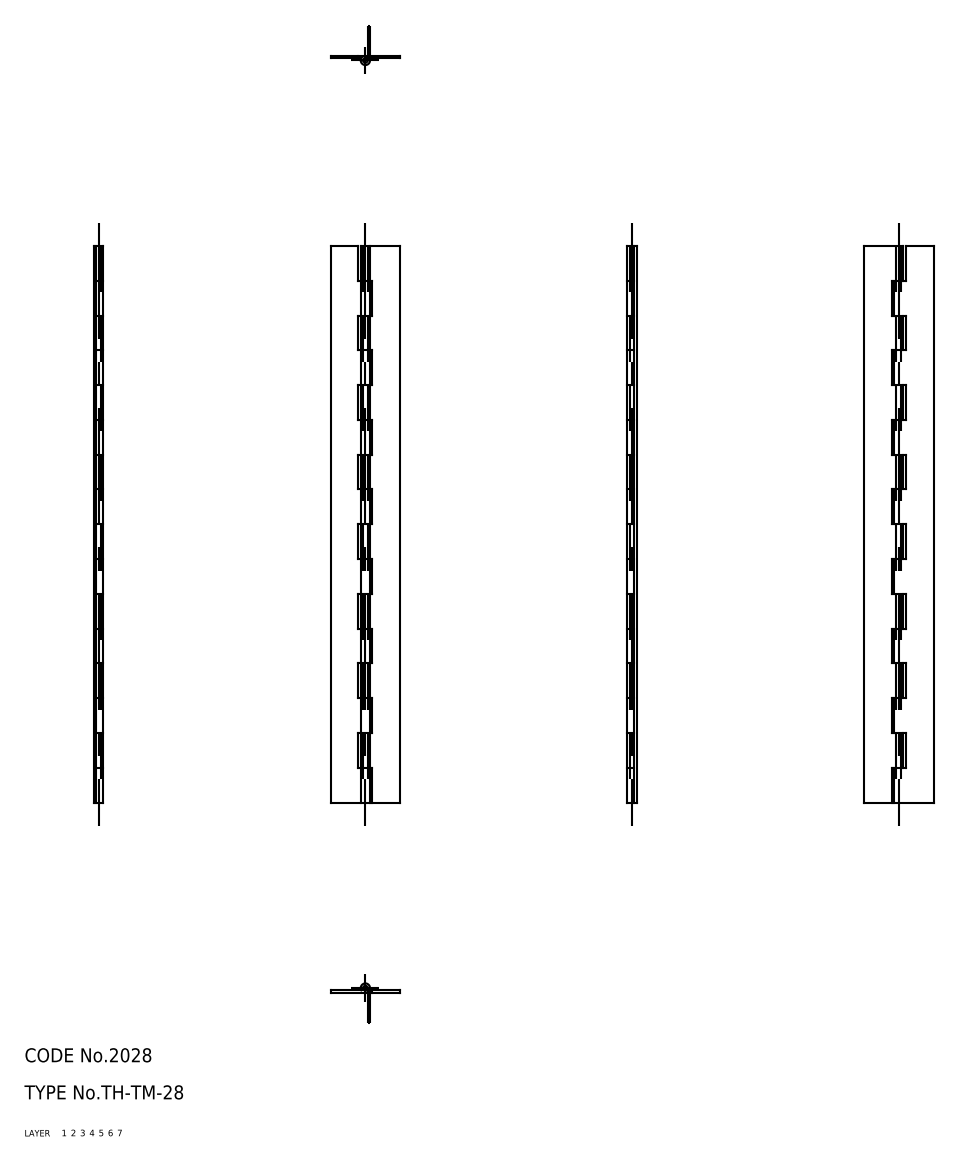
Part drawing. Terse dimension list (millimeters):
name: hinge piece_B; hinge piece_A; shaft; TH_TM_28_22376_36
written by: CADfix (AUTOMOTIVE_DESIGN)
unit: mm
bodies: 3 solids, 108 faces (0 planar, 0 cylindrical, 108 other)
size: 120 × 15 × 2
volume: 1 137 mm³; area: 4 889 mm²
